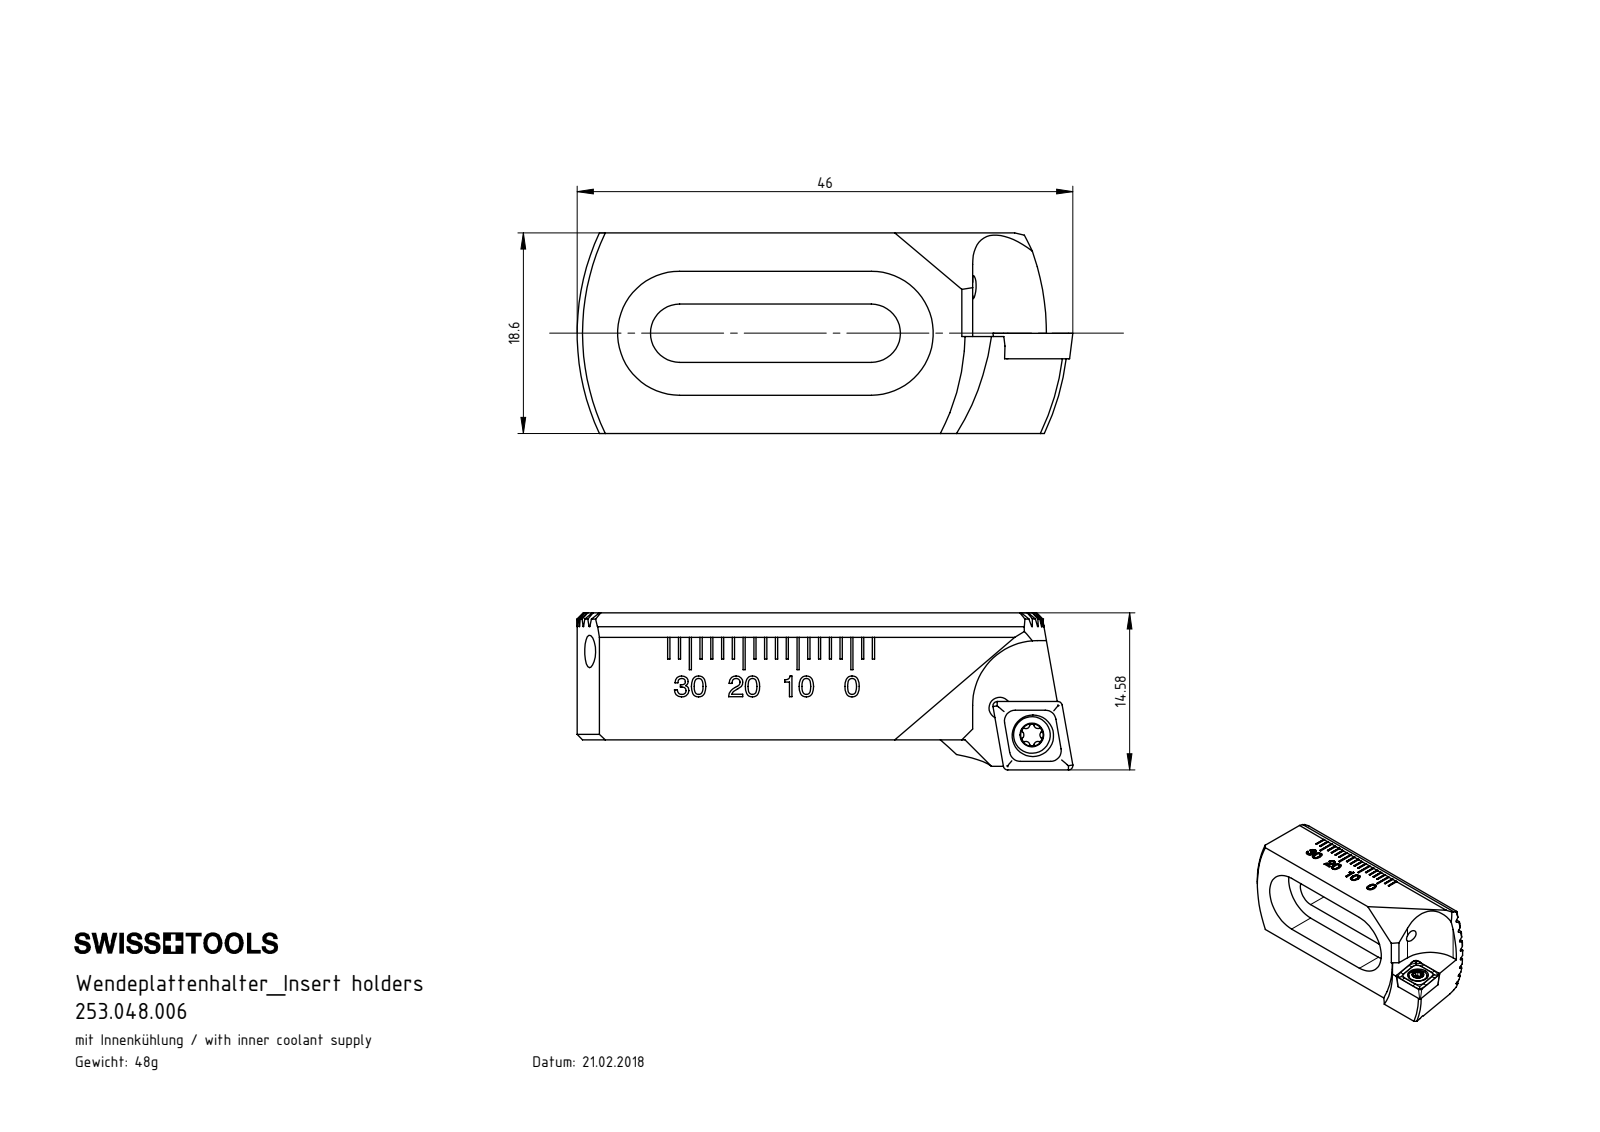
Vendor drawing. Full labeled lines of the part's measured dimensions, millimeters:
Part name (STEP PRODUCT): WCA-ER2.001.006_A; CCMT060204; BV2-WCA.K11.014_B; 253.048.006 (+1 more)
STEP written by: SolidWorks 2017 (CONFIG_CONTROL_DESIGN)
Units: millimetres
Bodies: 5 solids, 436 faces (208 planar, 76 cylindrical, 152 other)
Overall size (bounding box): 46 × 18.6 × 14.58
Volume: 6 019 mm³ · Surface area: 4 319 mm²
Round holes (diameter × count): ⌀2 ×4, ⌀2.05 ×1, ⌀2.38 ×1, ⌀2.8 ×1, ⌀3.85 ×1
Round bosses / shafts (diameter × count): ⌀3.4 ×1, ⌀3 ×1, ⌀2.5 ×1
Partial cylindrical surfaces — rounded edges, fillets, slot ends (radius × count): R0.14 ×10, R0.21 ×6, R0.36 ×5, R2.7 ×2, R5.75 ×2, R0.36 ×1, R6 ×1, R22 ×1
Main face-to-face distances: 1.73, 3.46, 8.66, 10.39, 6.93, 18.6, 12.12, 12, 6.6, 5.2
Hole centre spacings: 3.89, 4
